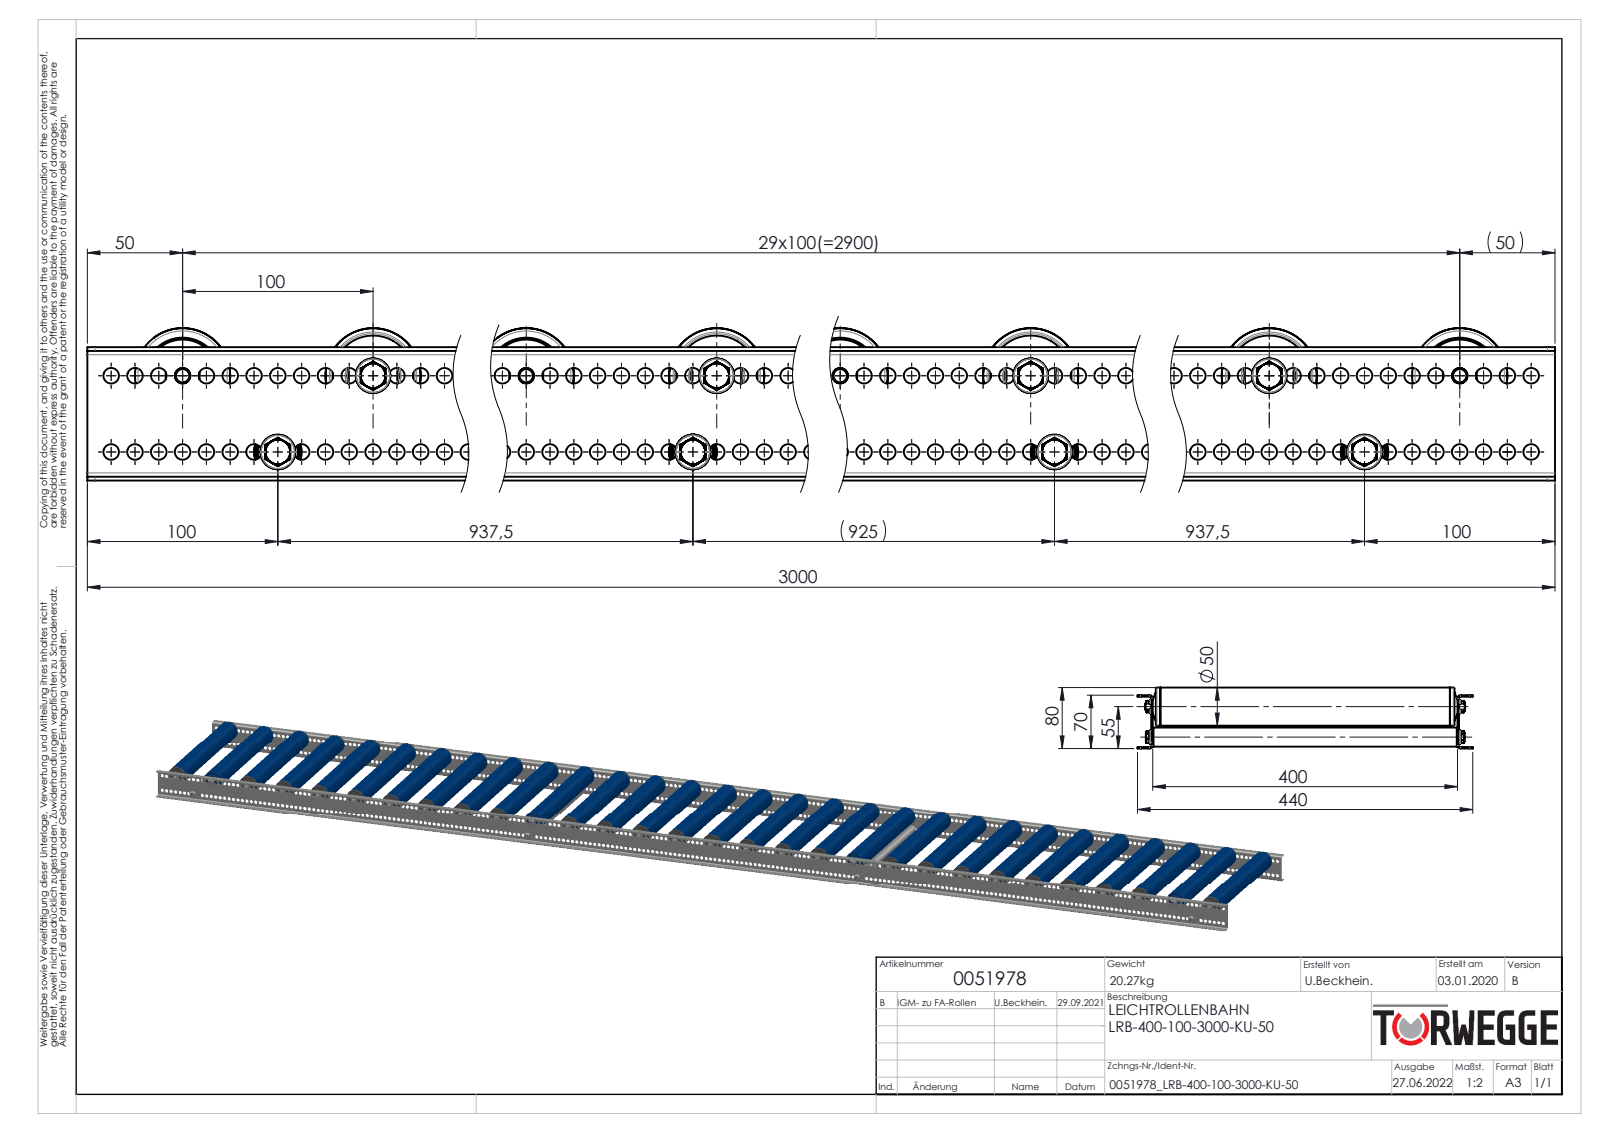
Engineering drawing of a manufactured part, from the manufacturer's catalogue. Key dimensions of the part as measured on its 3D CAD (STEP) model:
Part name (STEP PRODUCT): 0024178_Passscheibe_DIN988_12x18x1; Profil_LRB-20x70x20x2_KFG_S109080_U-PROFIL-20-70-20-2-LRB-L=3000; Druckfeder_1,2x10x30; 0051978 (+8 more)
STEP written by: SolidWorks 2020 (AUTOMOTIVE_DESIGN)
Units: millimetres
Bodies: 529 solids, 10474 faces (2574 planar, 4860 cylindrical, 3040 other)
Overall size (bounding box): 3000 × 440 × 80
Volume: 8 578 000 mm³ · Surface area: 6 523 000 mm²
Round holes (diameter × count): ⌀8.2 ×478, ⌀7.6 ×26, ⌀8 ×26, ⌀25 ×26, ⌀30 ×26, ⌀35 ×26, ⌀39.4 ×26, ⌀40 ×26, ⌀6.8 ×8, ⌀12 ×4, ⌀12.1 ×4, ⌀16 ×4
Round bosses / shafts (diameter × count): ⌀50 ×30, ⌀44.4 ×26, ⌀38 ×26, ⌀36 ×26, ⌀33 ×26, ⌀22 ×26, ⌀21 ×26, ⌀25 ×8
Partial cylindrical surfaces — rounded edges, fillets, slot ends (radius × count): R0.6 ×52, R0.75 ×52, R2.45 ×52, R4.87 ×26, R7 ×26, R2.5 ×16, R4 ×8, R2 ×4
Main face-to-face distances: 2, 402, 68, 400, 404, 70, 66, 392, 6, 12
Hole centre spacings: 12.5, 25, 37.5, 50, 62.5, 75, 87.5, 100
